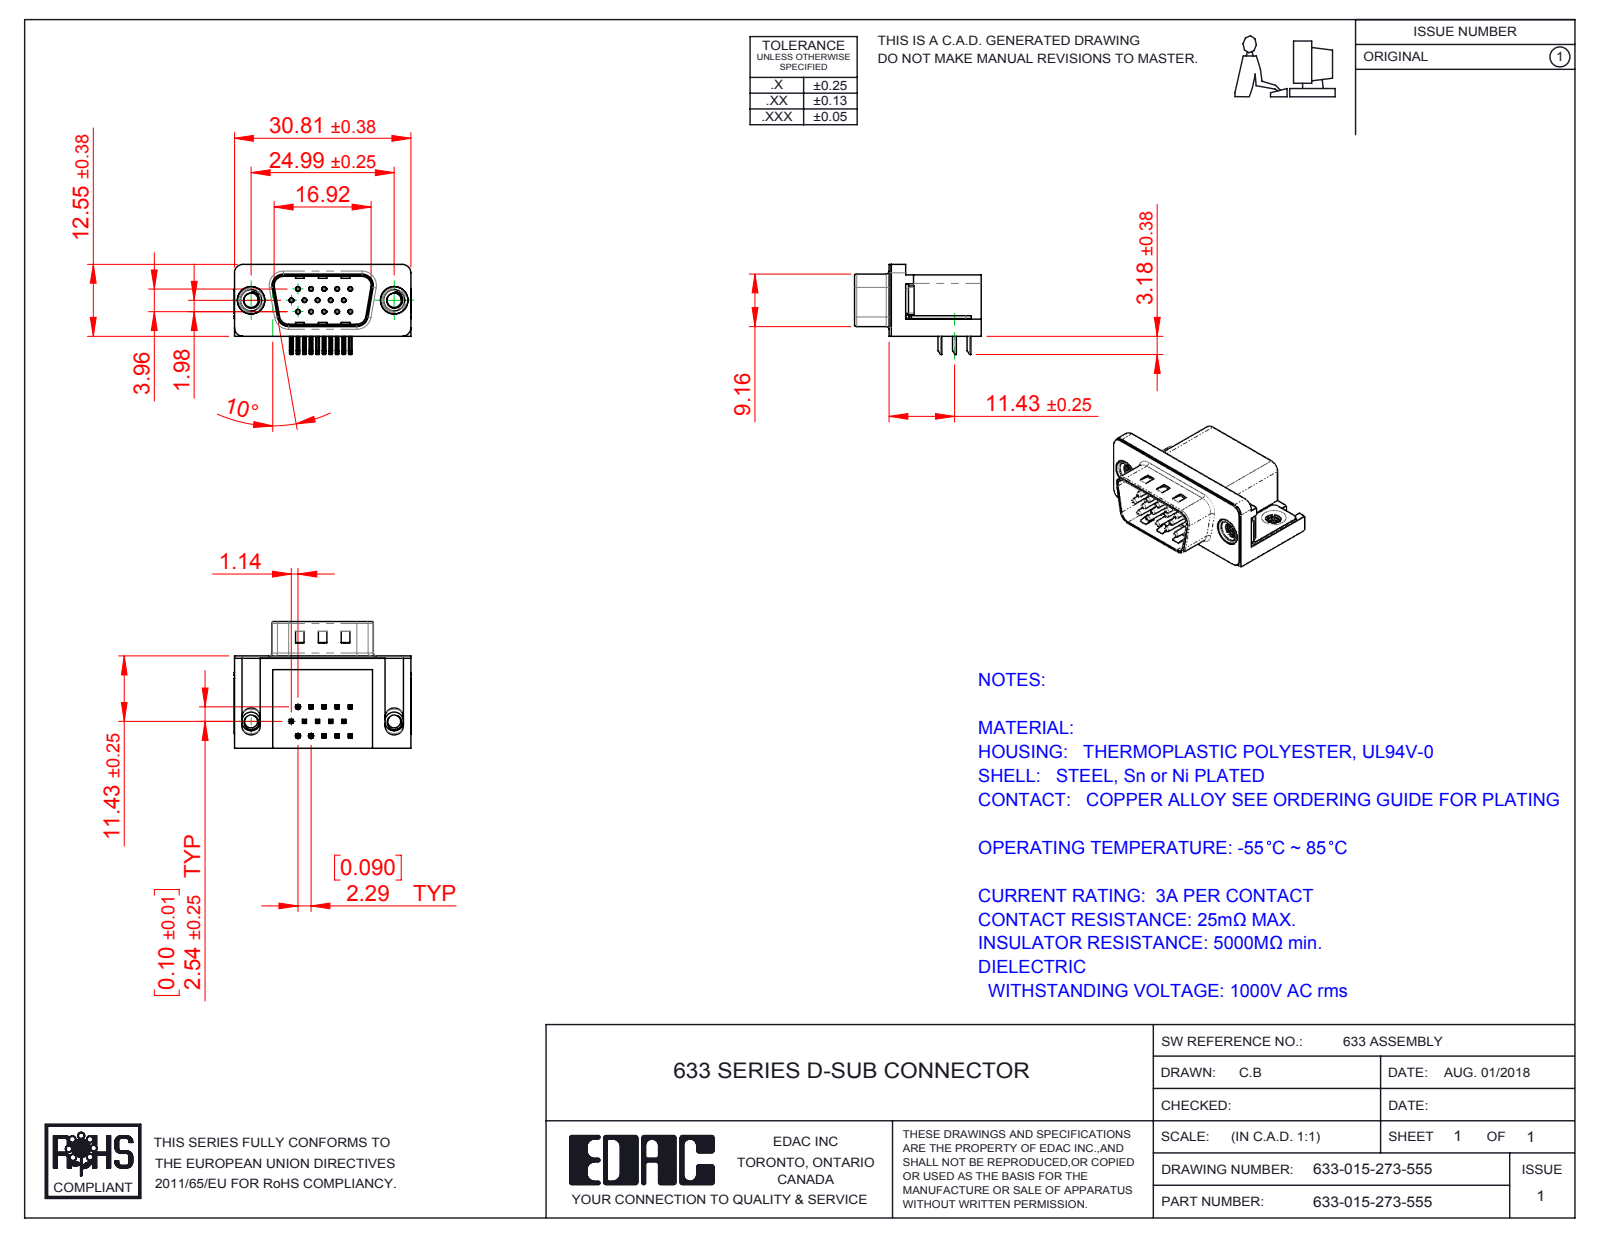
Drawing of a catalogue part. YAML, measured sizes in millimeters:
part_name: "633 4-40 Threaded Board Mount; 633 Contact Top; 633 M3 Threaded Rivet; 633-015-273-555 (+5 more)"
step_written_by: "SolidWorks 2016 (CONFIG_CONTROL_DESIGN)"
units: millimeters
bodies: {solids: 21, faces: 1473, planar: 861, cylindrical: 459, other: 153}
overall_size: [30.89, 22.1, 15.73]
volume: 4079
surface_area: 5505
round_holes:
  - {diameter: 0.35, count: 15}
  - {diameter: 0.8, count: 15}
  - {diameter: 2.26, count: 2}
  - {diameter: 2.5, count: 2}
  - {diameter: 4, count: 2}
  - {diameter: 4.8, count: 2}
  - {diameter: 5, count: 2}
round_bosses_or_shafts:
  - {diameter: 0.75, count: 15}
  - {diameter: 4.9, count: 2}
  - {diameter: 4.75, count: 2}
  - {diameter: 3.9, count: 2}
  - {diameter: 3.26, count: 2}
partial_cylinders:
  - {radius: 0.25, count: 68}
  - {radius: 0.12, count: 30}
  - {radius: 1, count: 16}
  - {radius: 0.5, count: 9}
  - {radius: 1.6, count: 8}
  - {radius: 1.5, count: 7}
  - {radius: 0.9, count: 4}
  - {radius: 2, count: 4}
face_to_face_distances: [0.4, 10.35, 15.7, 2.9, 6.7, 16.1, 2.5, 0.5, 0.35, 10.7]
hole_center_spacings: [3.96, 2.28, 4.57, 2.29, 6.05, 6.86, 7.92, 6.04]
